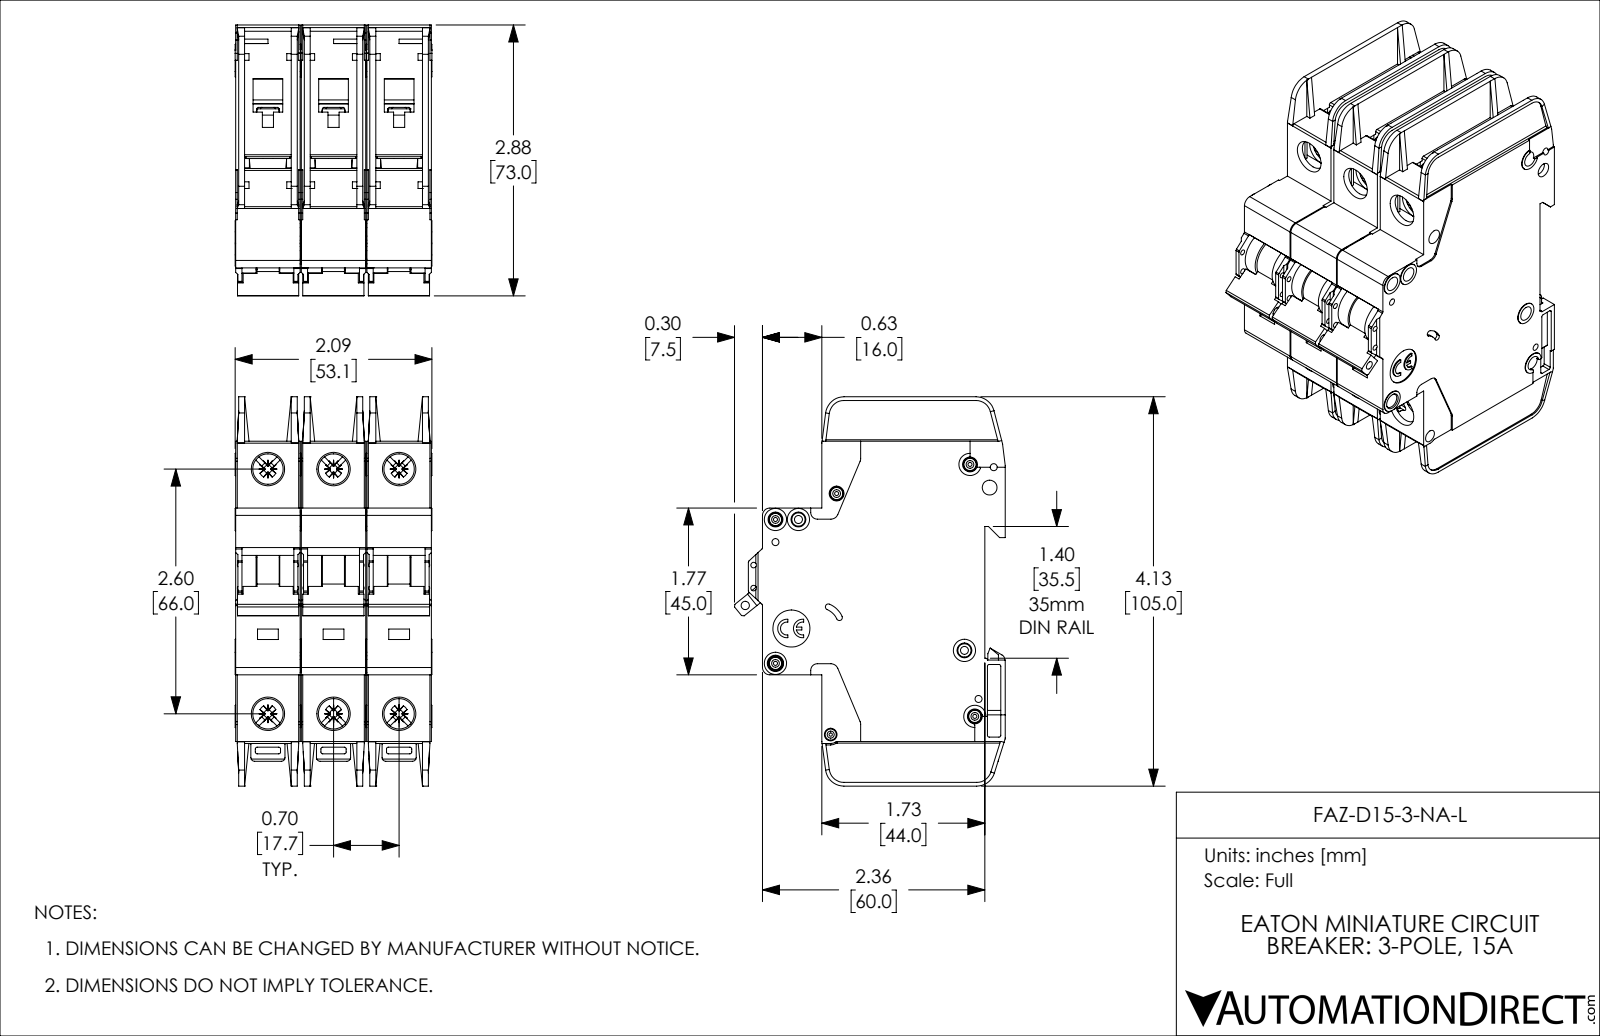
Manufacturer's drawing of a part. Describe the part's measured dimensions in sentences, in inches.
The part is named "FAZ-D15-3-NA-L". Its 3-D file was written by "SolidWorks 2019 (AUTOMOTIVE_DESIGN)". It is 3 solids with 3381 faces: 2013 planar, 1071 cylindrical and 297 other. Overall it measures 4.134 by 2.876 by 2.091 inches. Its volume is 14.05 cubic inches and its surface area 123 square inches. Round holes: 8 of diameter 0.157, 6 of diameter 0.323, 5 of diameter 0.043, 4 of diameter 0.075, 2 of diameter 0.059, 2 of diameter 0.085, 1 of diameter 0.035, 1 of diameter 0.089, 1 of diameter 0.098, 1 of diameter 0.134, 1 of diameter 0.394. Round bosses or shafts: 5 of diameter 0.13, 4 of diameter 0.236, 4 of diameter 0.118, 3 of diameter 0.098. Partial cylindrical surfaces (rounded edges, fillets, slot ends): 72 of radius 0.02, 30 of radius 0.016, 18 of radius 0.039, 12 of radius 0.043, 12 of radius 0.079, 6 of radius 0.008, 6 of radius 0.01, 6 of radius 0.028. The main face-to-face distances are 0.697, 0.047, 1.394, 0.685, 0.591, 1.382, 0.744, 0.65, 0.106, 0.094. The hole center spacings are 0.697, 2.69, 2.598, 0.244, 0.537, 0.87, 1.394, 2.948.
